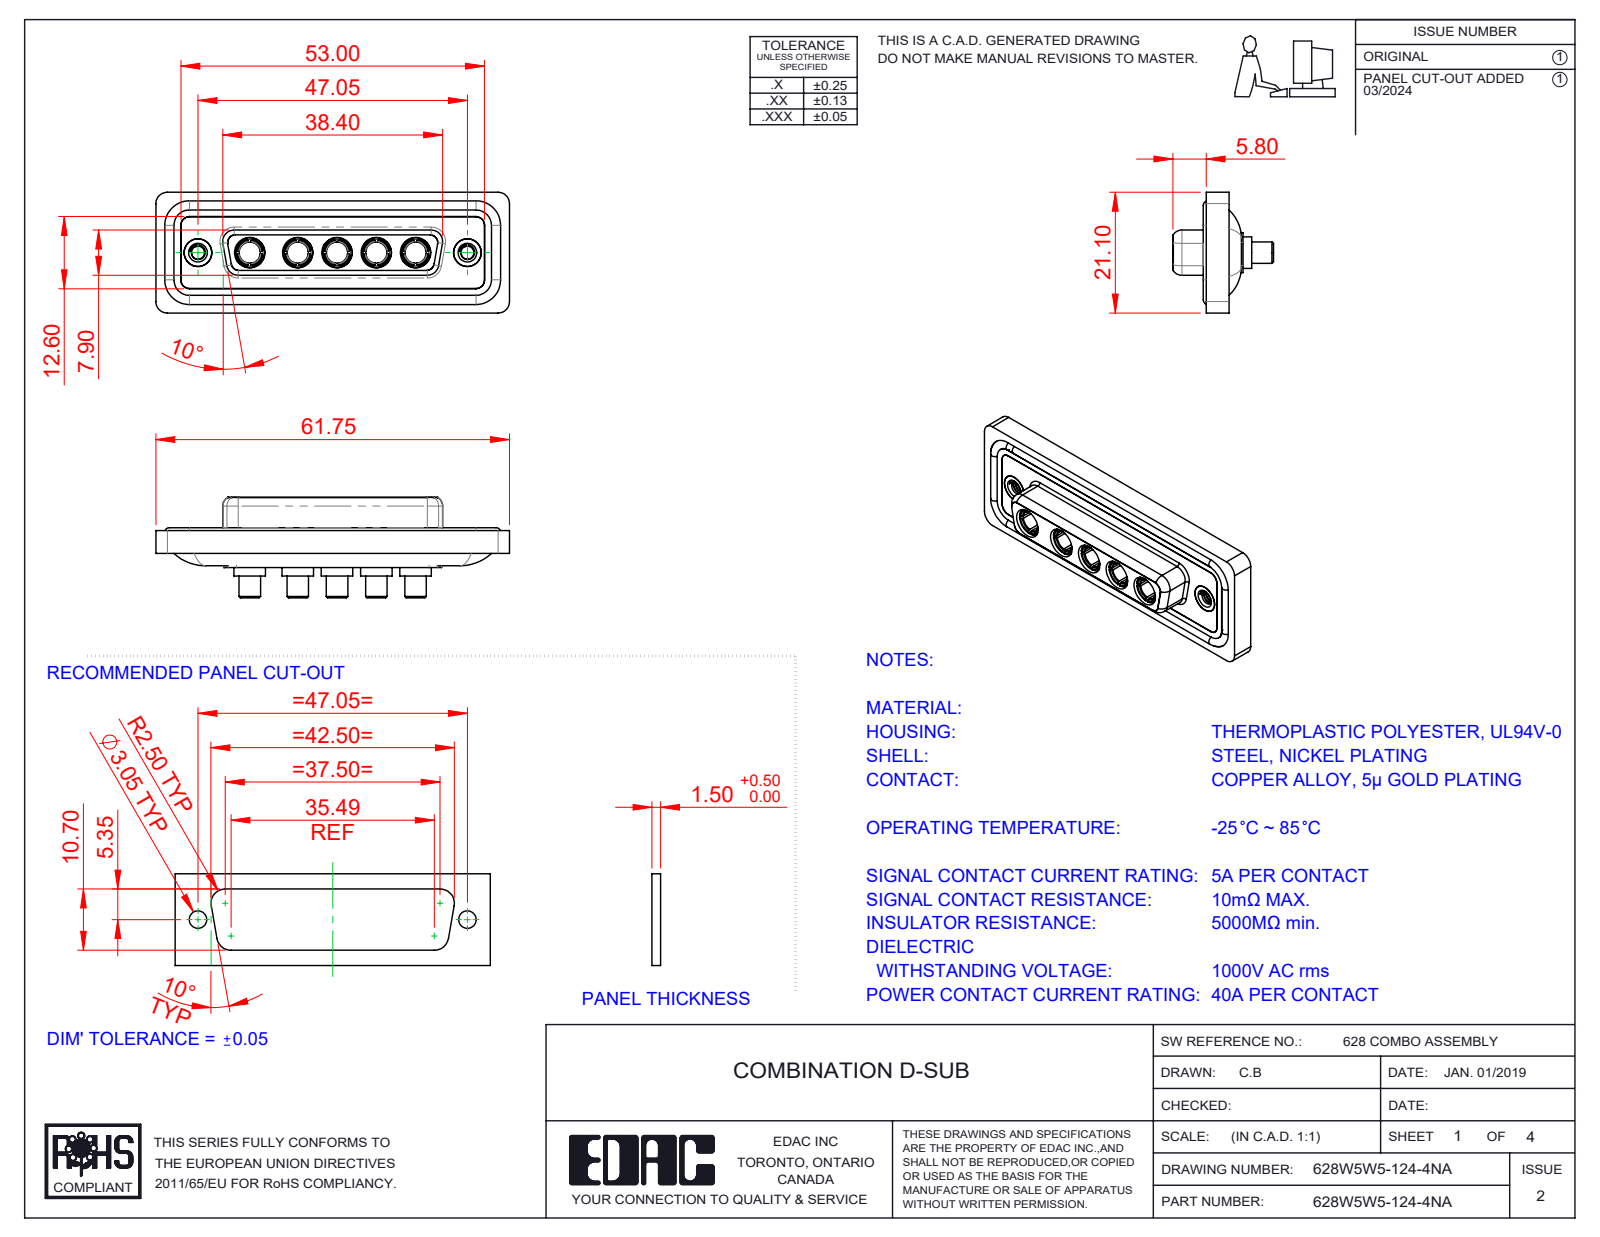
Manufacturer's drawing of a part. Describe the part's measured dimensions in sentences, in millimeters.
The part is named "628Combo Shell Rear_25 Contacts; 628Combo Waterproof Housing_25 Contacts; 628Combo Housing_5W5; Power Socket_40A S (+3 more)". Its 3-D file was written by "SolidWorks 2023 (CONFIG_CONTROL_DESIGN)". It is 17 solids with 754 faces: 250 planar, 305 cylindrical and 199 other. Overall it measures 61.75 by 21.1 by 17.55 millimeters. Its volume is 8 267 cubic millimeters and its surface area 13 467 square millimeters. Round holes: 7 of diameter 4.85, 5 of diameter 3.7, 5 of diameter 5.3, 2 of diameter 2.26, 2 of diameter 4, 2 of diameter 4.05, 2 of diameter 5. Round bosses or shafts: 5 of diameter 5.5, 5 of diameter 5.2, 5 of diameter 4.96, 5 of diameter 4.75, 5 of diameter 3.75, 4 of diameter 1.6, 2 of diameter 4.95, 2 of diameter 4.8. Partial cylindrical surfaces (rounded edges, fillets, slot ends): 22 of radius 1.5, 18 of radius 2, 8 of radius 1.35, 8 of radius 1.6, 5 of radius 2.1, 4 of radius 0.25, 4 of radius 0.5, 4 of radius 0.6. The main face-to-face distances are 0.4, 1.8, 7.45, 5.65, 0.5, 7.05, 6.6, 1.6, 1.1, 2.9. The hole center spacings are 6.86, 9.04, 13.72, 38.01, 8.39, 15.25, 15.9, 17.43.
